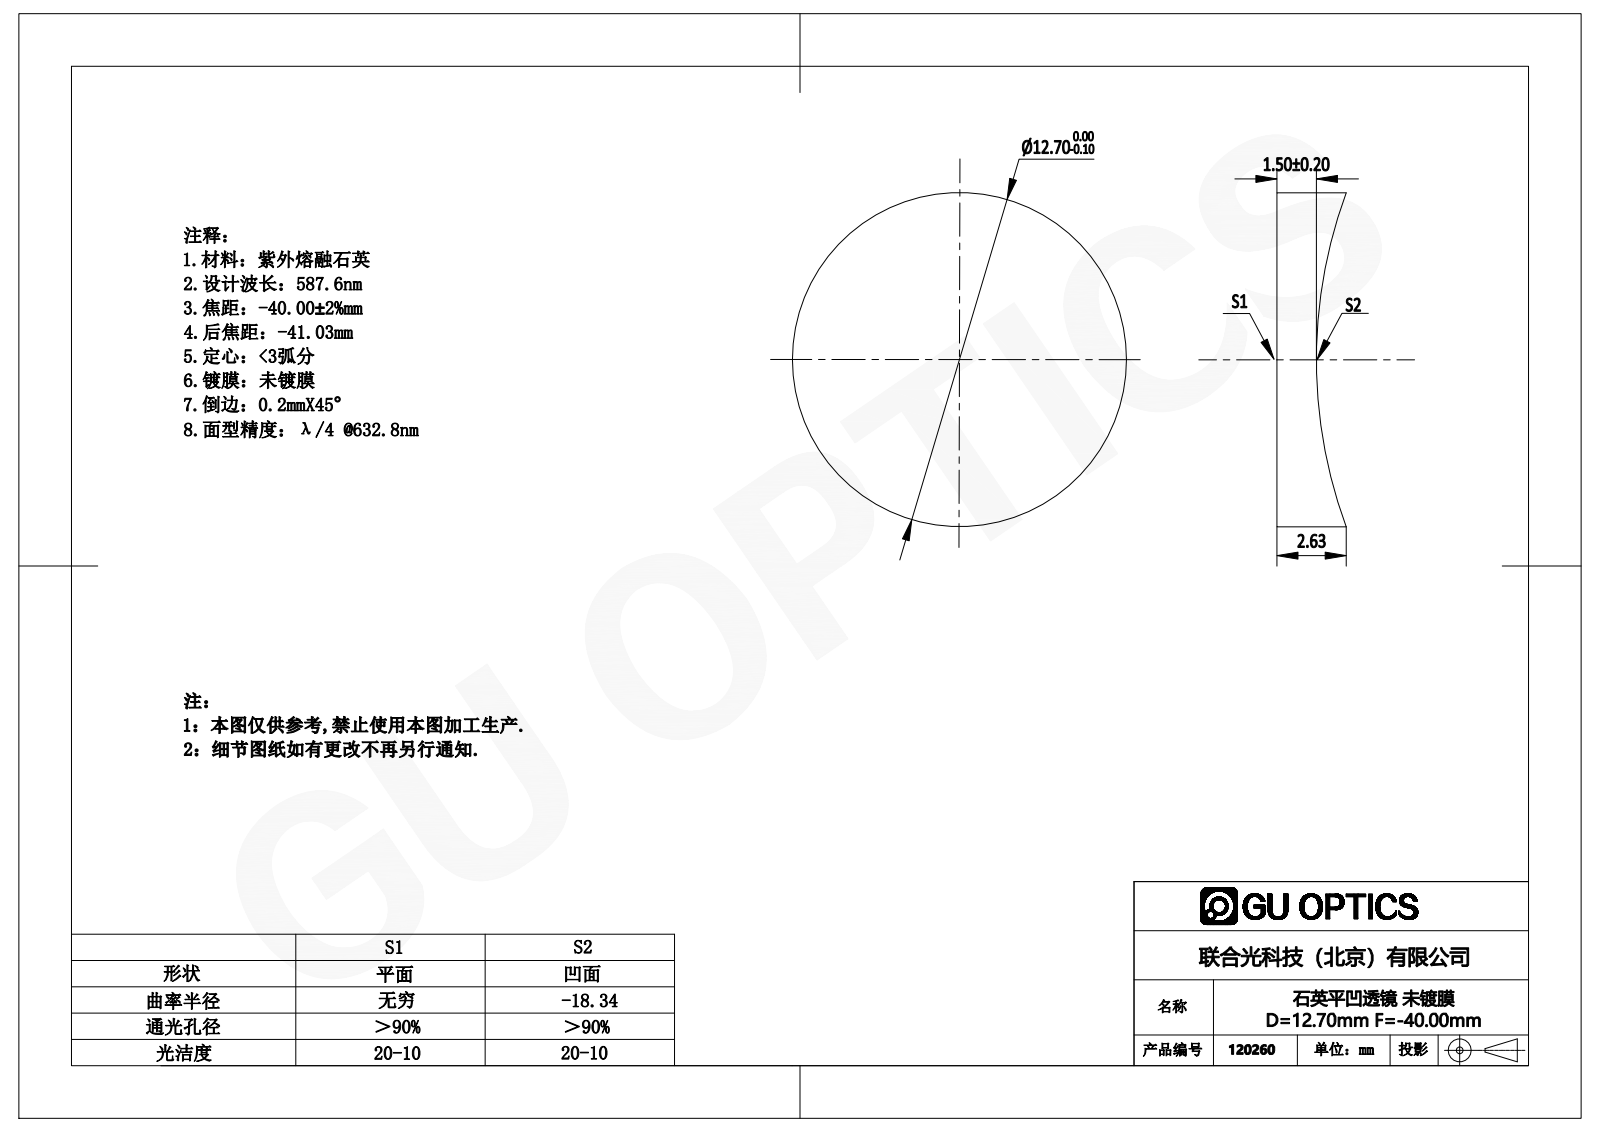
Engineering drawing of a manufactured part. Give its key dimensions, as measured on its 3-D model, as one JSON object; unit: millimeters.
{"part_name": "120260", "step_written_by": "SolidWorks 2016 (AUTOMOTIVE_DESIGN)", "units": "millimeters", "bodies": {"solids": 1, "faces": 5, "planar": 1, "cylindrical": 2, "other": 2}, "overall_size": [12.7, 12.7, 2.63], "volume_mm3": 261, "surface_area_mm2": 362, "round_bosses_or_shafts": [[12.7, 1]]}
